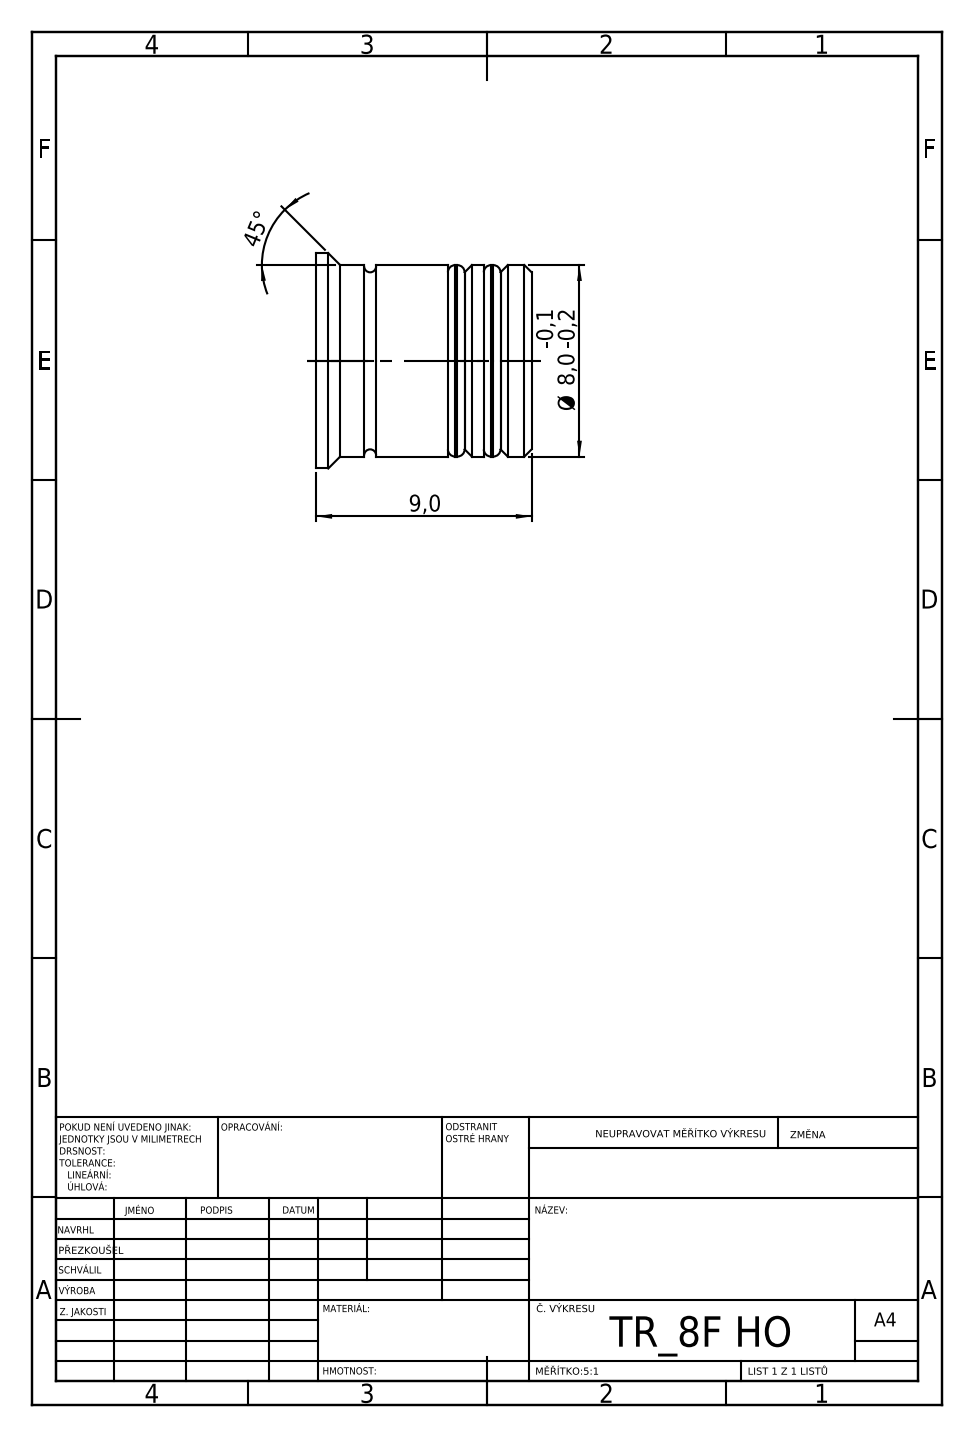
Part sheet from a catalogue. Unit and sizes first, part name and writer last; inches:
Units: inches
Overall size (bounding box): 0.354 × 0.354 × 0.354
Round bosses / shafts (diameter × count): ⌀0.354 ×1, ⌀0.315 ×1, ⌀0.291 ×1, ⌀0.197 ×1
Main face-to-face distances: 0.059, 0.028, 0.079, 0.138, 0.051, 0.087, 0.11, 0.031, 0.039, 0.236
Volume: 0.03 in³ · Surface area: 0.994 in²
Bodies: 3 solids, 72 faces (30 planar, 20 cylindrical, 22 other)
STEP written by: SolidWorks 2019 (CONFIG_CONTROL_DESIGN)
